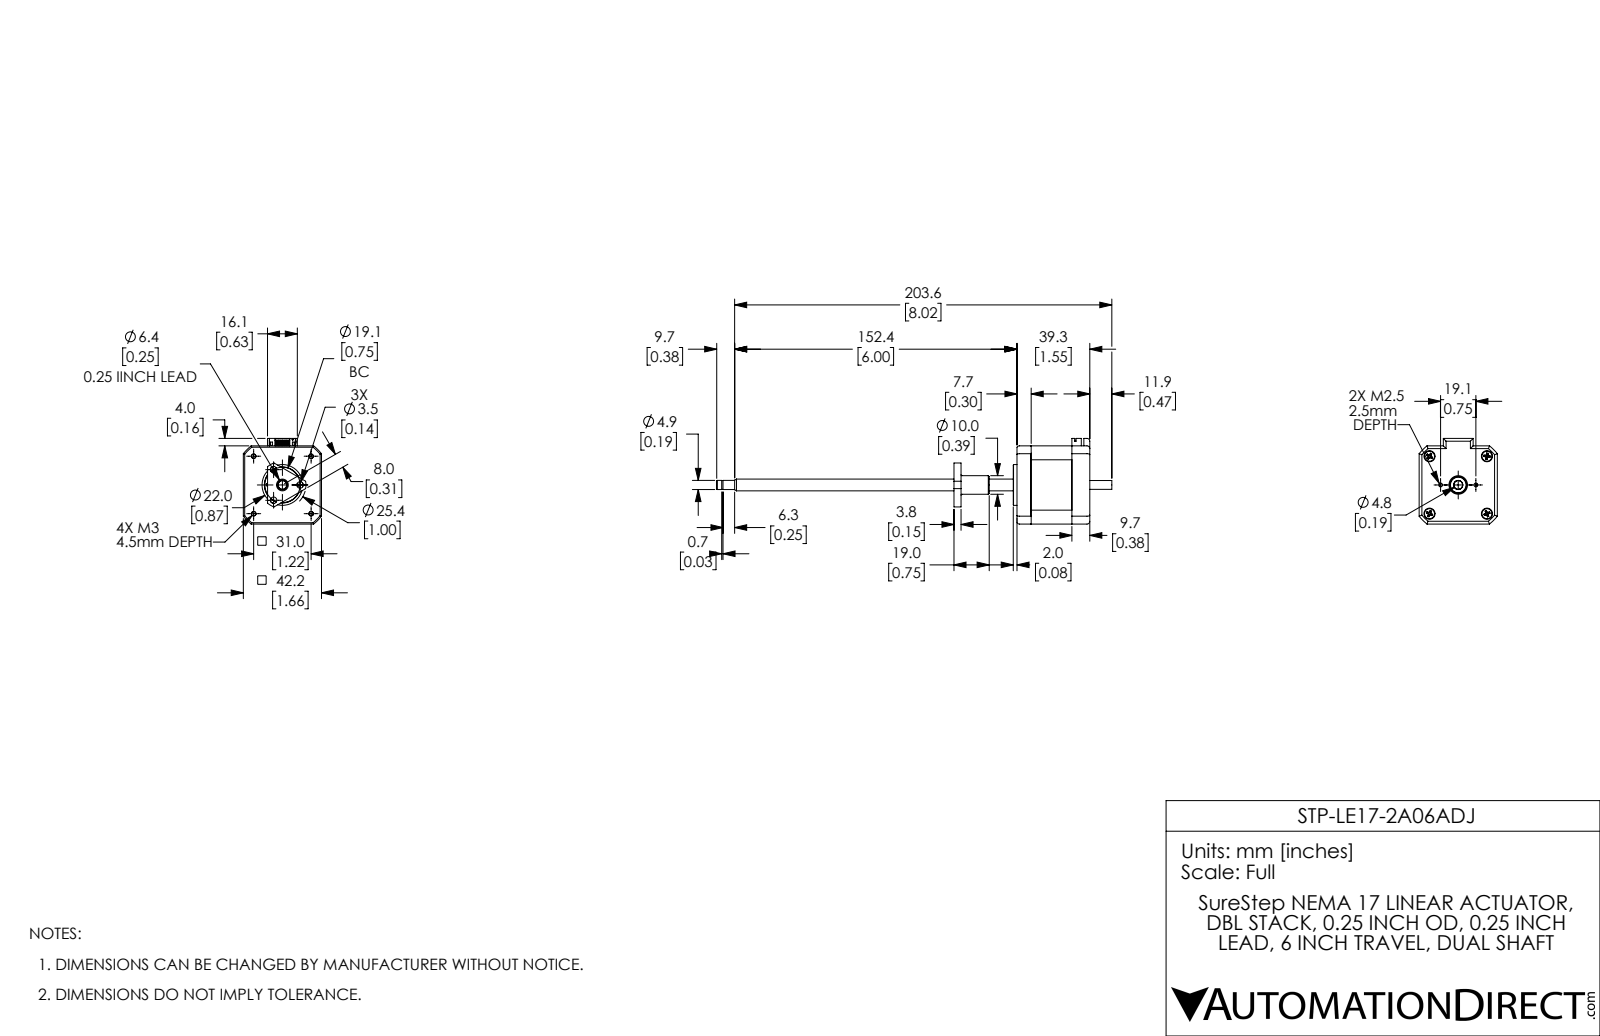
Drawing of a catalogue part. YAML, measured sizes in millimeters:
part_name: "STP-LE17-2A06ADJ; STP-LE17-2A06ADJ_2; STP-LE17-2A06ADJ_1"
step_written_by: "SolidWorks 2017 (AUTOMOTIVE_DESIGN)"
units: millimeters
bodies: {solids: 6, faces: 740, planar: 364, cylindrical: 240, other: 136}
overall_size: [213.25, 46.2, 42.2]
volume: 64368
surface_area: 28526
round_holes:
  - {diameter: 2.5, count: 4}
  - {diameter: 3.8, count: 4}
  - {diameter: 6, count: 4}
  - {diameter: 3.5, count: 3}
  - {diameter: 1.5, count: 2}
  - {diameter: 2.05, count: 2}
  - {diameter: 4.9, count: 1}
  - {diameter: 5, count: 1}
  - {diameter: 13, count: 1}
  - {diameter: 17, count: 1}
  - {diameter: 19.46, count: 1}
  - {diameter: 20, count: 1}
round_bosses_or_shafts:
  - {diameter: 5.4, count: 4}
  - {diameter: 2.91, count: 4}
  - {diameter: 27, count: 1}
  - {diameter: 25.91, count: 1}
  - {diameter: 22, count: 1}
  - {diameter: 12, count: 1}
  - {diameter: 10, count: 1}
  - {diameter: 9, count: 1}
partial_cylinders:
  - {radius: 1, count: 12}
  - {radius: 1.5, count: 11}
  - {radius: 2.5, count: 2}
  - {radius: 0.7, count: 1}
  - {radius: 12.7, count: 1}
  - {radius: 14.25, count: 1}
  - {radius: 16, count: 1}
  - {radius: 25.1, count: 1}
face_to_face_distances: [42.2, 9.65, 39.3, 29.65, 31.65, 1.6, 22, 7.65, 1, 36.8]
hole_center_spacings: [16.61, 9.52, 21.92, 29.43, 31, 4.93, 8, 12.96]
